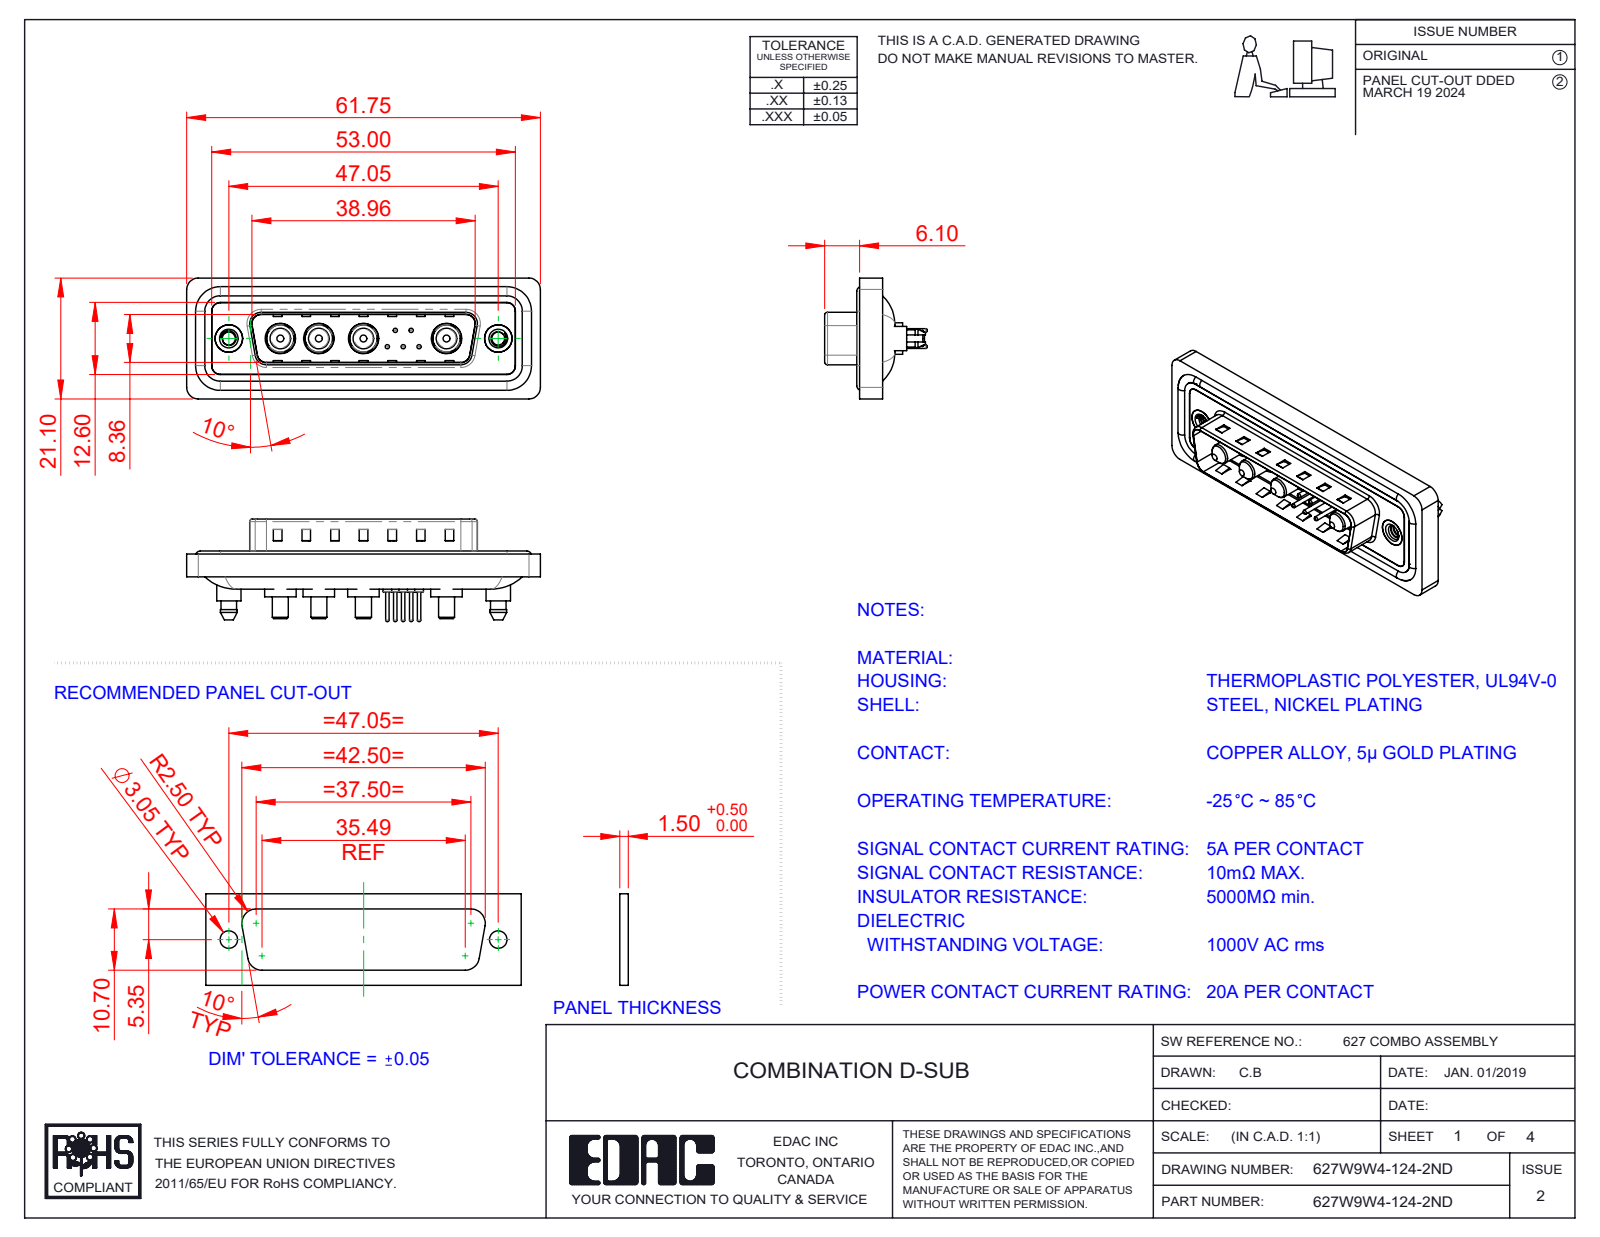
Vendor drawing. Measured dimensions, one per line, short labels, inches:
name: 627Combo Threaded Boardlock_5; 627Combo Threaded Boardlock_D; 627Combo Shell Front_25 Contacts; 627Combo Shell Rear_25 Contacts (+6 more)
written by: SolidWorks 2023 (CONFIG_CONTROL_DESIGN)
unit: in
bodies: 20 solids, 882 faces (300 planar, 374 cylindrical, 208 other)
size: 2.431 × 0.831 × 0.705
volume: 0.46 in³; area: 18.87 in²
holes: 5× ⌀0.03, 5× ⌀0.063, 5× ⌀0.079, 4× ⌀0.191, 4× ⌀0.209, 2× ⌀0.089, 2× ⌀0.157, 2× ⌀0.189, 2× ⌀0.197
bosses: 5× ⌀0.059, 5× ⌀0.024, 4× ⌀0.217, 4× ⌀0.205, 4× ⌀0.187, 4× ⌀0.148, 4× ⌀0.142, 4× ⌀0.11
rounds: 24× R0.059, 18× R0.079, 10× R0.063, 8× R0.02, 4× R0.01, 4× R0.024, 4× R0.026, 4× R0.035
face distances: 0.016, 0.059, 0.043, 0.02, 0.122, 0.063, 0.114, 0.032, 0.377, 0.222
hole spacings: 0.124, 0.109, 0.198, 0.571, 0.109, 0.173, 0.174, 0.197
